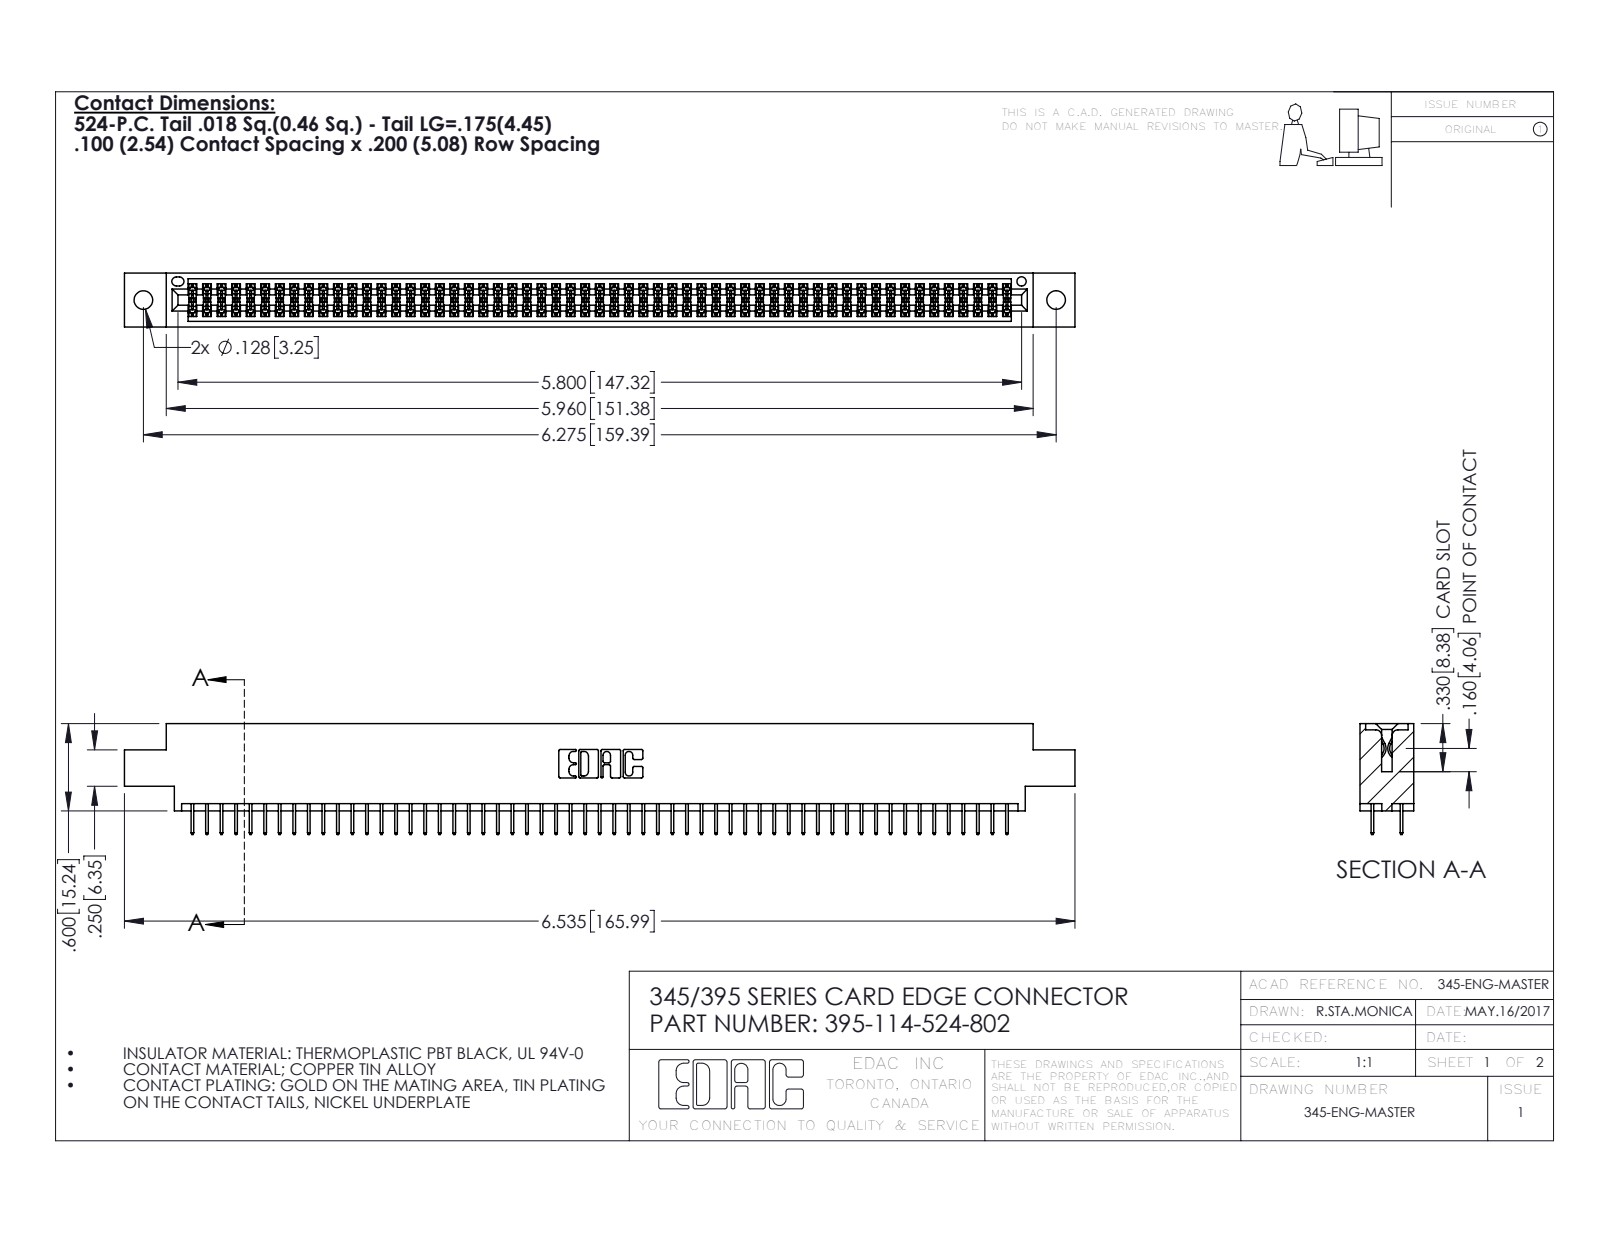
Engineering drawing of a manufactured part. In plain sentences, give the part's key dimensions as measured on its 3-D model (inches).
The part is named "395-114-524-802; 345 Part_0.170 Offset - 0.128 Dia; 345-292-001_345-293-124". Its 3-D file was written by "SolidWorks 2016 (CONFIG_CONTROL_DESIGN)". It is 115 solids with 6286 faces: 4530 planar, 1756 cylindrical and 0 other. Overall it measures 6.535 by 0.762 by 0.37 inches. Its volume is 0.973 cubic inches and its surface area 36.07 square inches. Round holes: 2 of diameter 0.128, 1 of diameter 0.064. Partial cylindrical surfaces (rounded edges, fillets, slot ends): 171 of radius 0.006, 22 of radius 0.01, 6 of radius 0.007, 6 of radius 0.031, 3 of radius 0.026, 2 of radius 0.014, 2 of radius 0.019, 2 of radius 0.022. The main face-to-face distances are 0.072, 0.298, 0.37, 0.2, 0.098, 0.272, 0.025, 0.225, 0.072, 0.175. The hole center spacings are 0.27, 6.039, 6.275.
